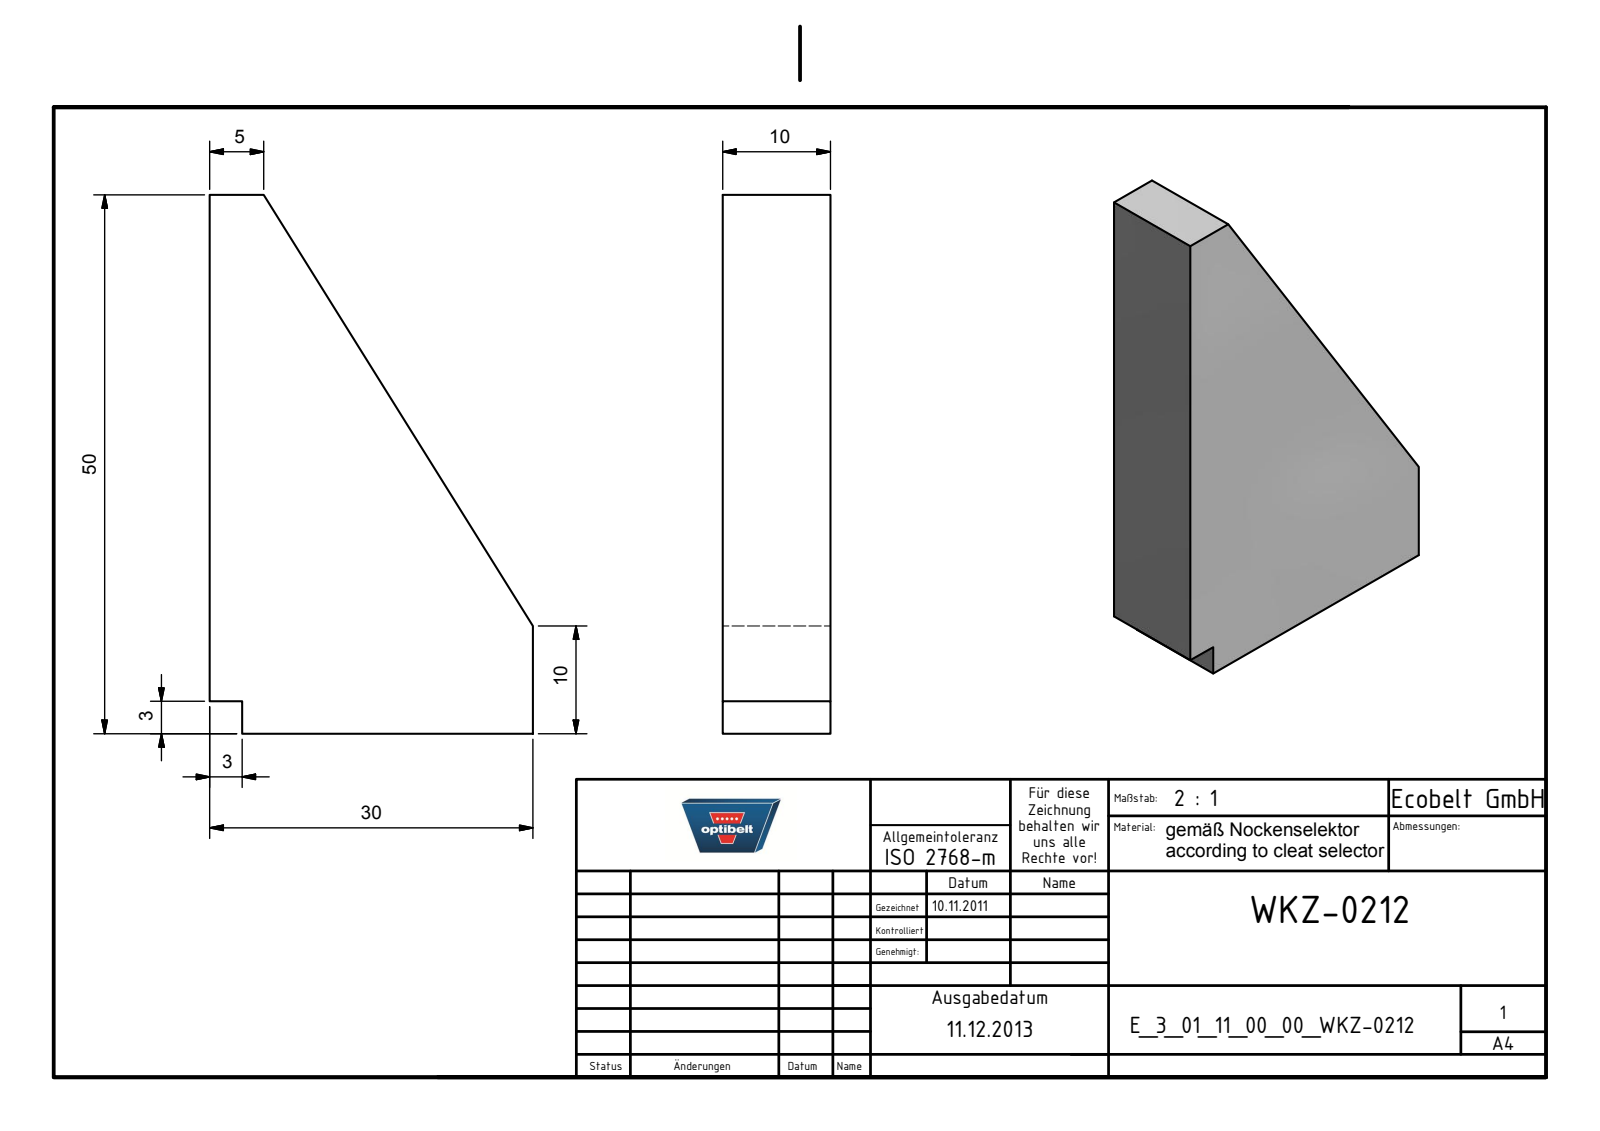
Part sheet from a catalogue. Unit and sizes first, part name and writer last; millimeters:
Units: millimetres
Overall size (bounding box): 50 × 30 × 10
Main face-to-face distances: 10, 30, 3, 50, 47, 27
Volume: 9 910 mm³ · Surface area: 3 404 mm²
Bodies: 1 solid, 9 faces (9 planar, 0 cylindrical, 0 other)
Part name (STEP PRODUCT): E_3_01_11_00_00_WKZ-0212
STEP written by: Autodesk Inventor 2025 (AUTOMOTIVE_DESIGN)
